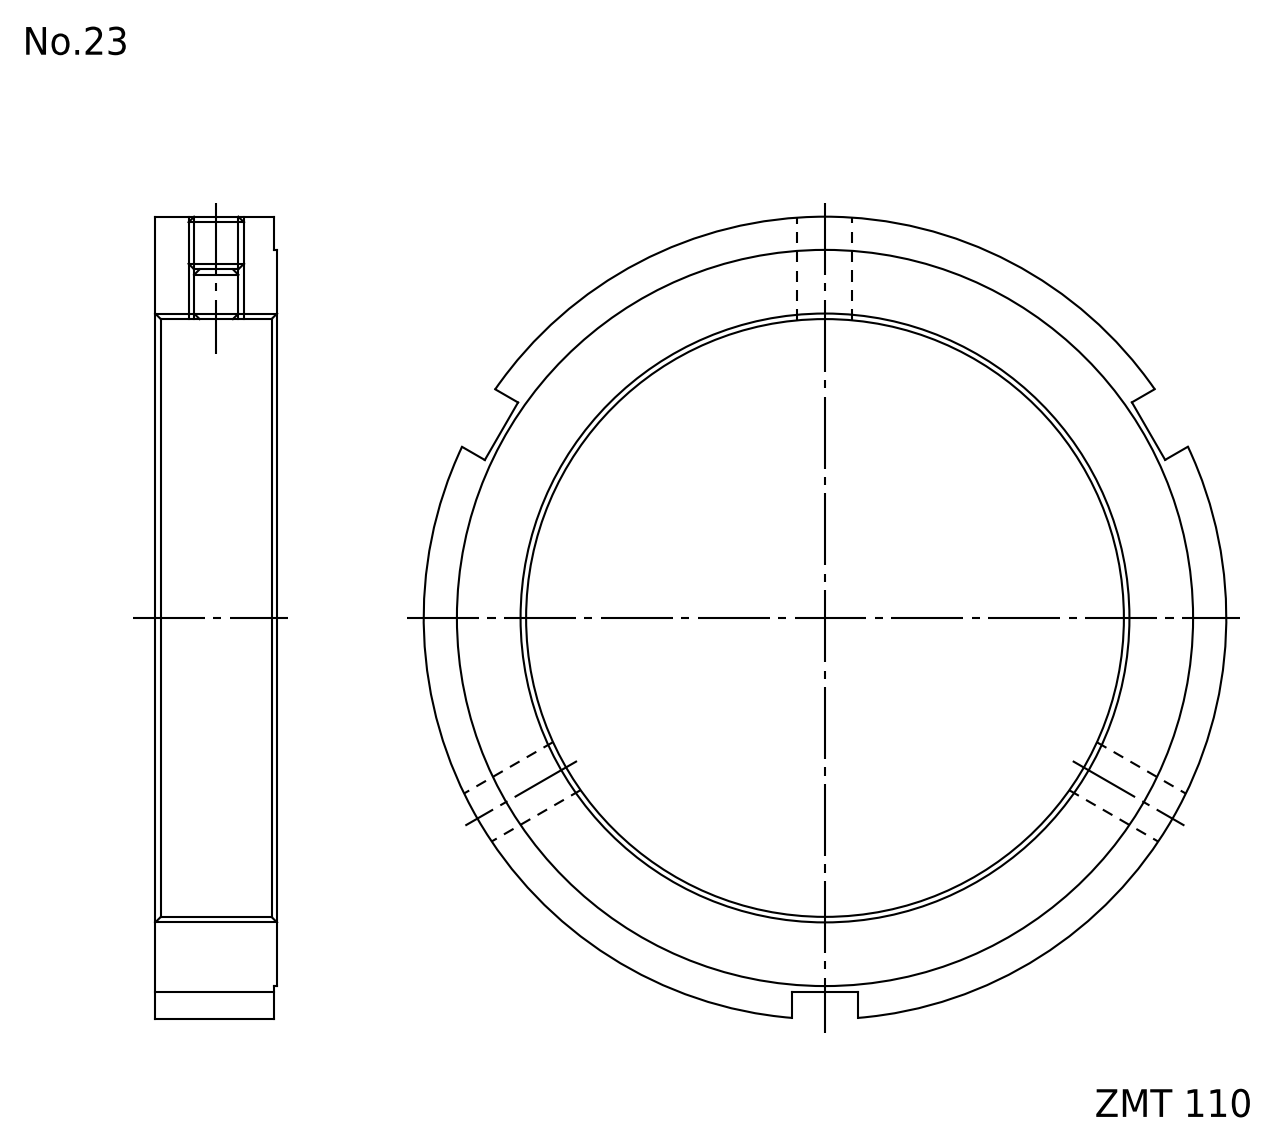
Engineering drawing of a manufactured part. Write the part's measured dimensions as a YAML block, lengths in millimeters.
part_name: "FKD ZMT110"
step_written_by: "Autodesk Inventor 2011 (AUTOMOTIVE_DESIGN)"
units: millimeters
bodies: {solids: 1, faces: 20, planar: 12, cylindrical: 8, other: 0}
overall_size: [145, 144.75, 22]
volume: 146204
surface_area: 32935
round_holes:
  - {diameter: 8.38, count: 3}
  - {diameter: 110, count: 1}
round_bosses_or_shafts:
  - {diameter: 145, count: 1}
  - {diameter: 133, count: 1}
face_to_face_distances: [22, 0.5, 21.5, 12]
